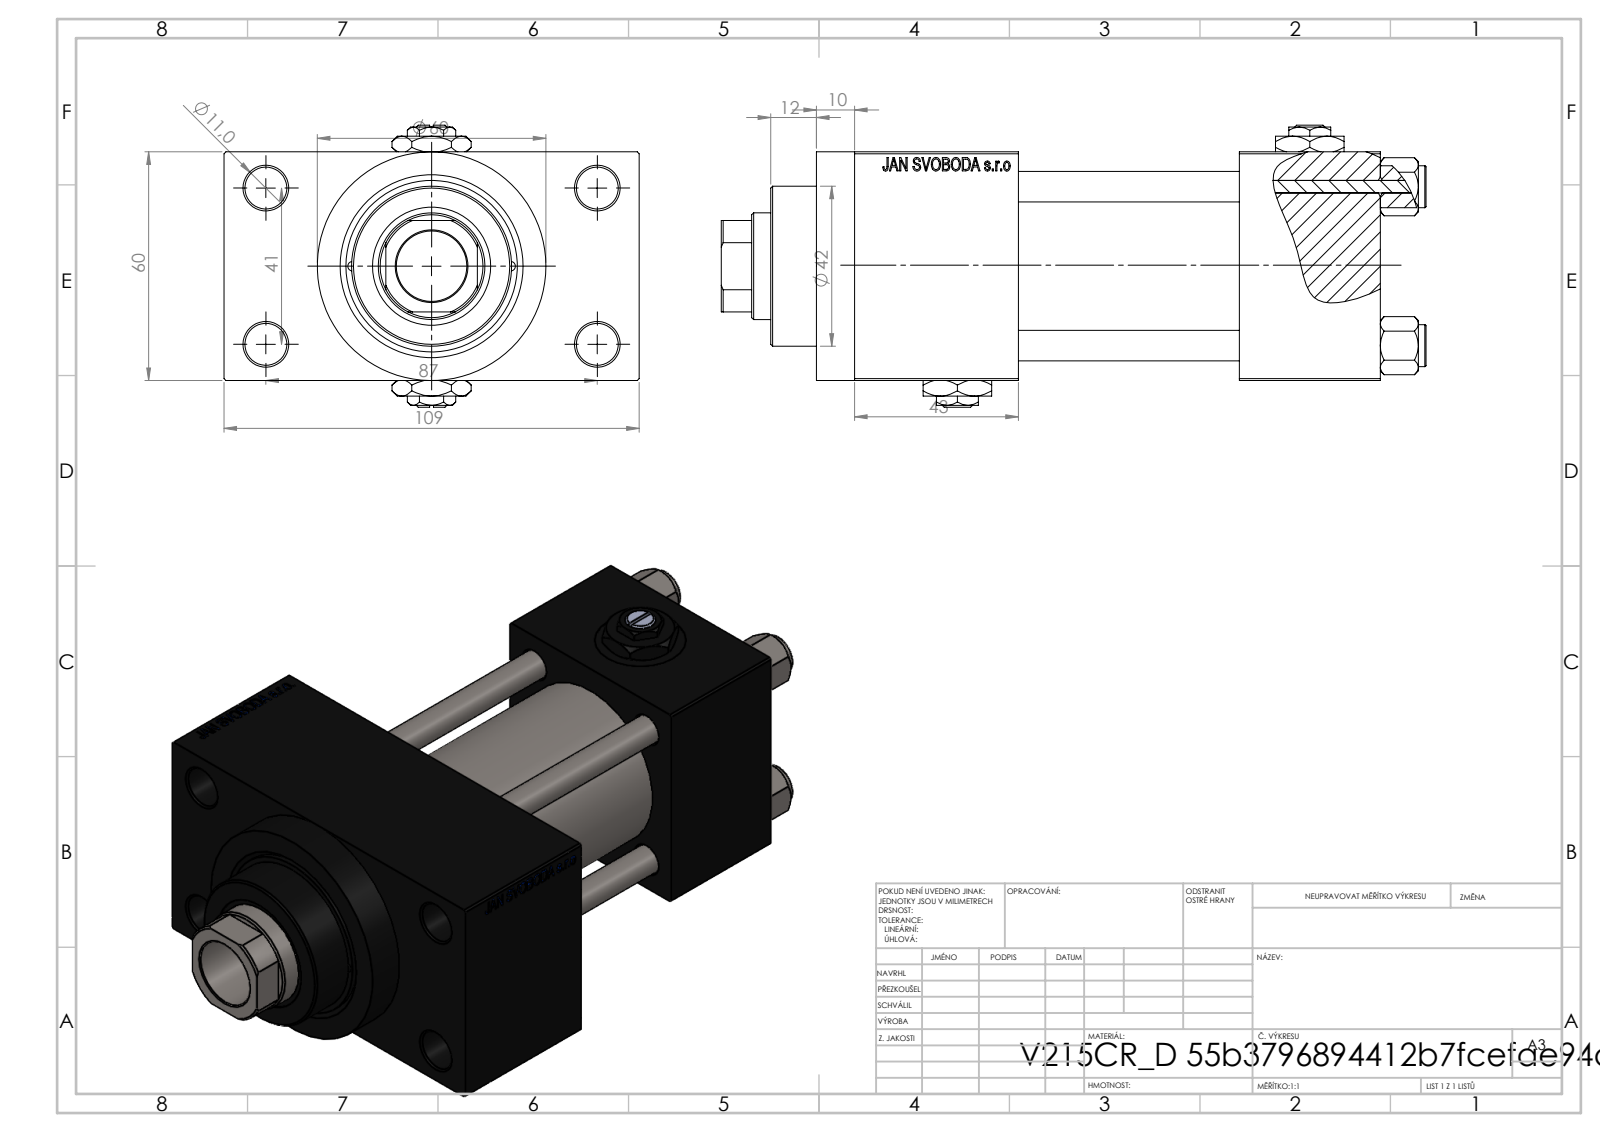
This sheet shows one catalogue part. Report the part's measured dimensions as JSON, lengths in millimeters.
{"part_name": "V215CR_VCP_D; V215CR_D_Body; Zatka_pro_OIL_PORT; V215CR_D_TYCINKA (+2 more)", "step_written_by": "SolidWorks 2019 (CONFIG_CONTROL_DESIGN)", "units": "millimeters", "bodies": {"solids": 13, "faces": 1199, "planar": 546, "cylindrical": 93, "other": 560}, "overall_size": [185, 109, 74], "volume_mm3": 536797, "surface_area_mm2": 129607, "round_holes": [[8, 4], [11, 4], [2.5, 2], [7, 2], [16.66, 2], [24, 2], [18.5, 1], [28, 1], [31, 1], [40, 1], [45, 1]], "round_bosses_or_shafts": [[11, 4], [60, 1], [46, 1], [42, 1]], "partial_cylinders_radius": [[13.5, 1]], "face_to_face_distances": [60, 84.5, 24.5, 58, 37, 95, 138, 101, 43, 109], "hole_center_spacings": [20.85, 22.65, 29.49, 30.62, 41.7, 46.53, 47.15, 48.09]}
